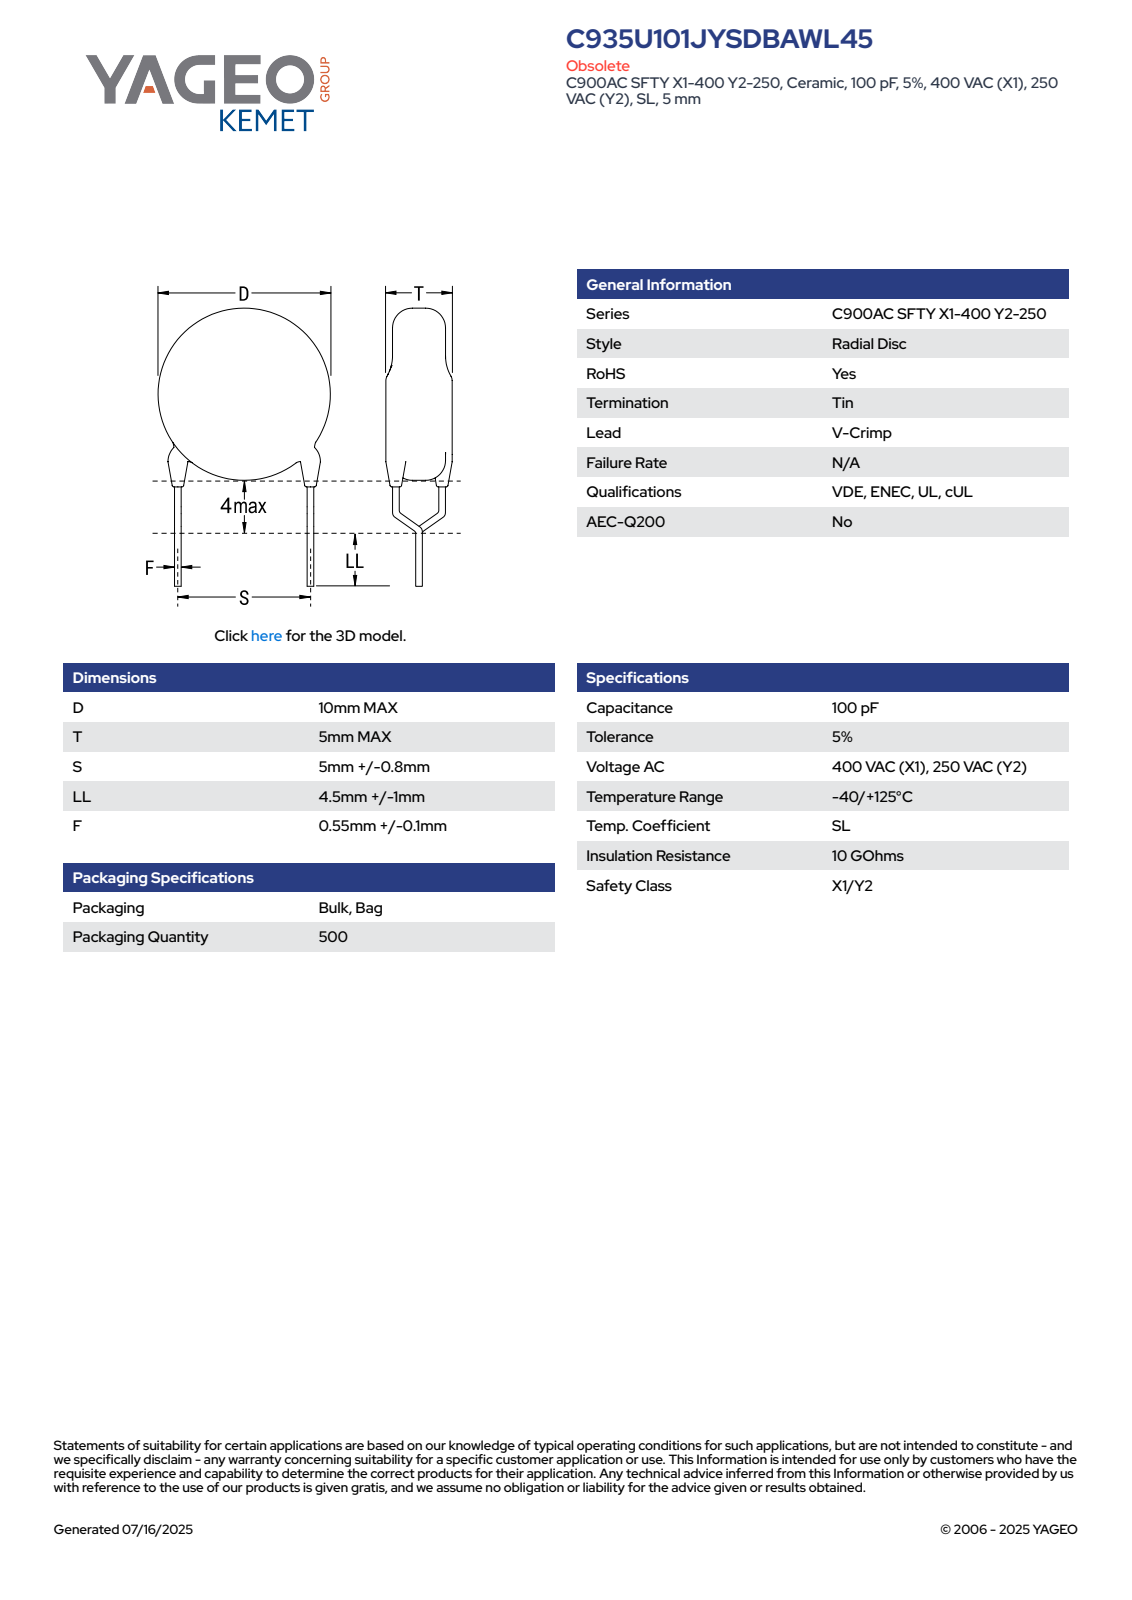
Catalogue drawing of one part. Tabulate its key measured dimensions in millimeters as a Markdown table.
| quantity | value |
| --- | --- |
| part name | CCD_VCC900_D10T5S5LL5.5F0.65 |
| STEP written by | SolidWorks 2014 (AUTOMOTIVE_DESIGN) |
| units | millimeters |
| bodies | 5 solids, 93 faces (65 planar, 16 cylindrical, 12 other) |
| overall size | 19.3 × 10 × 5 |
| volume | 387 mm³ |
| surface area | 341 mm² |
| round bosses / shafts (diameter × count) | 0.65 × 6, 10 × 1 |
| main face-to-face distances | 5, 8.4, 1.3, 14.95, 6.55, 13.65, 5.25, 0.32, 1.05, 2.68 |
